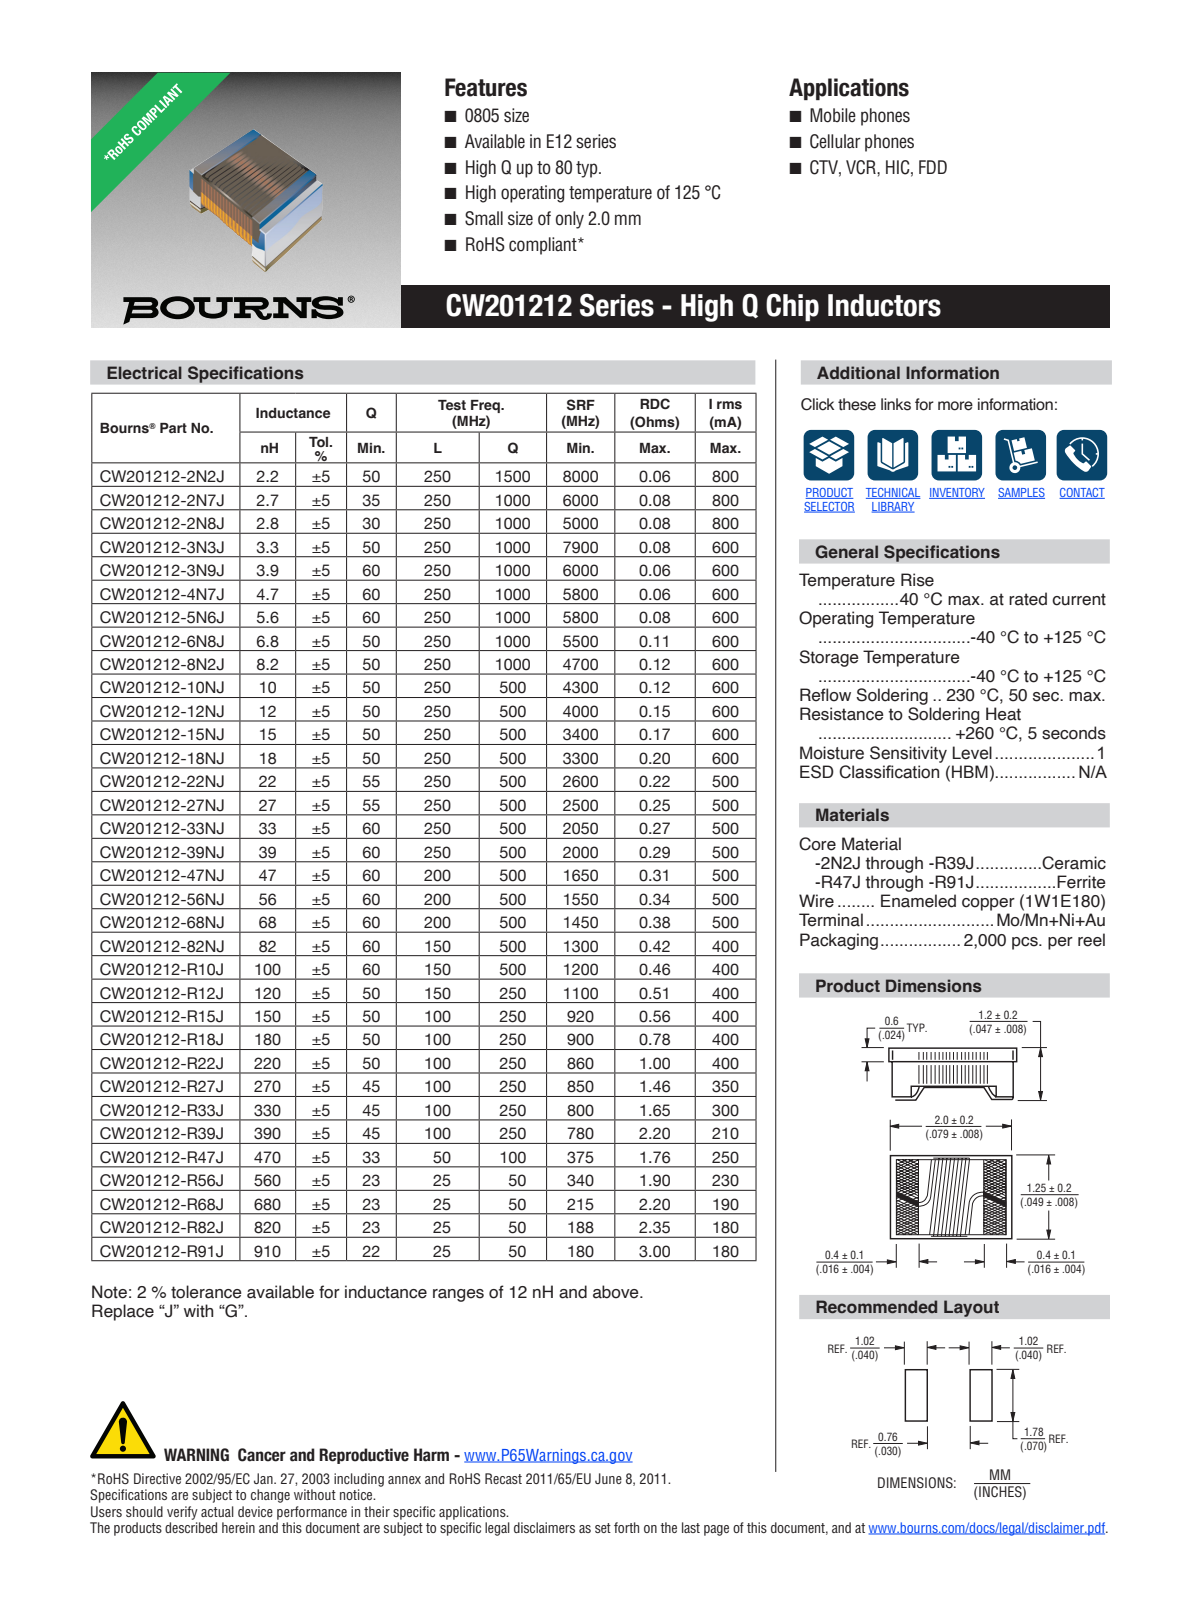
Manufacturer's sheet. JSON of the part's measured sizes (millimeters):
{"part_name": "CW201212", "step_written_by": "PRO/ENGINEER BY PARAMETRIC TECHNOLOGY CORPORATION, 2010100 (CONFIG_CONTROL_DESIGN)", "units": "millimeters", "bodies": {"solids": 1, "faces": 535, "planar": 223, "cylindrical": 208, "other": 104}, "overall_size": [2.1, 1.5, 1.3], "volume_mm3": 4, "surface_area_mm2": 17, "face_to_face_distances": [1.45, 2.05, 1.3, 1.5, 1.4, 2, 2.1, 1.22, 0.5, 0.8]}
